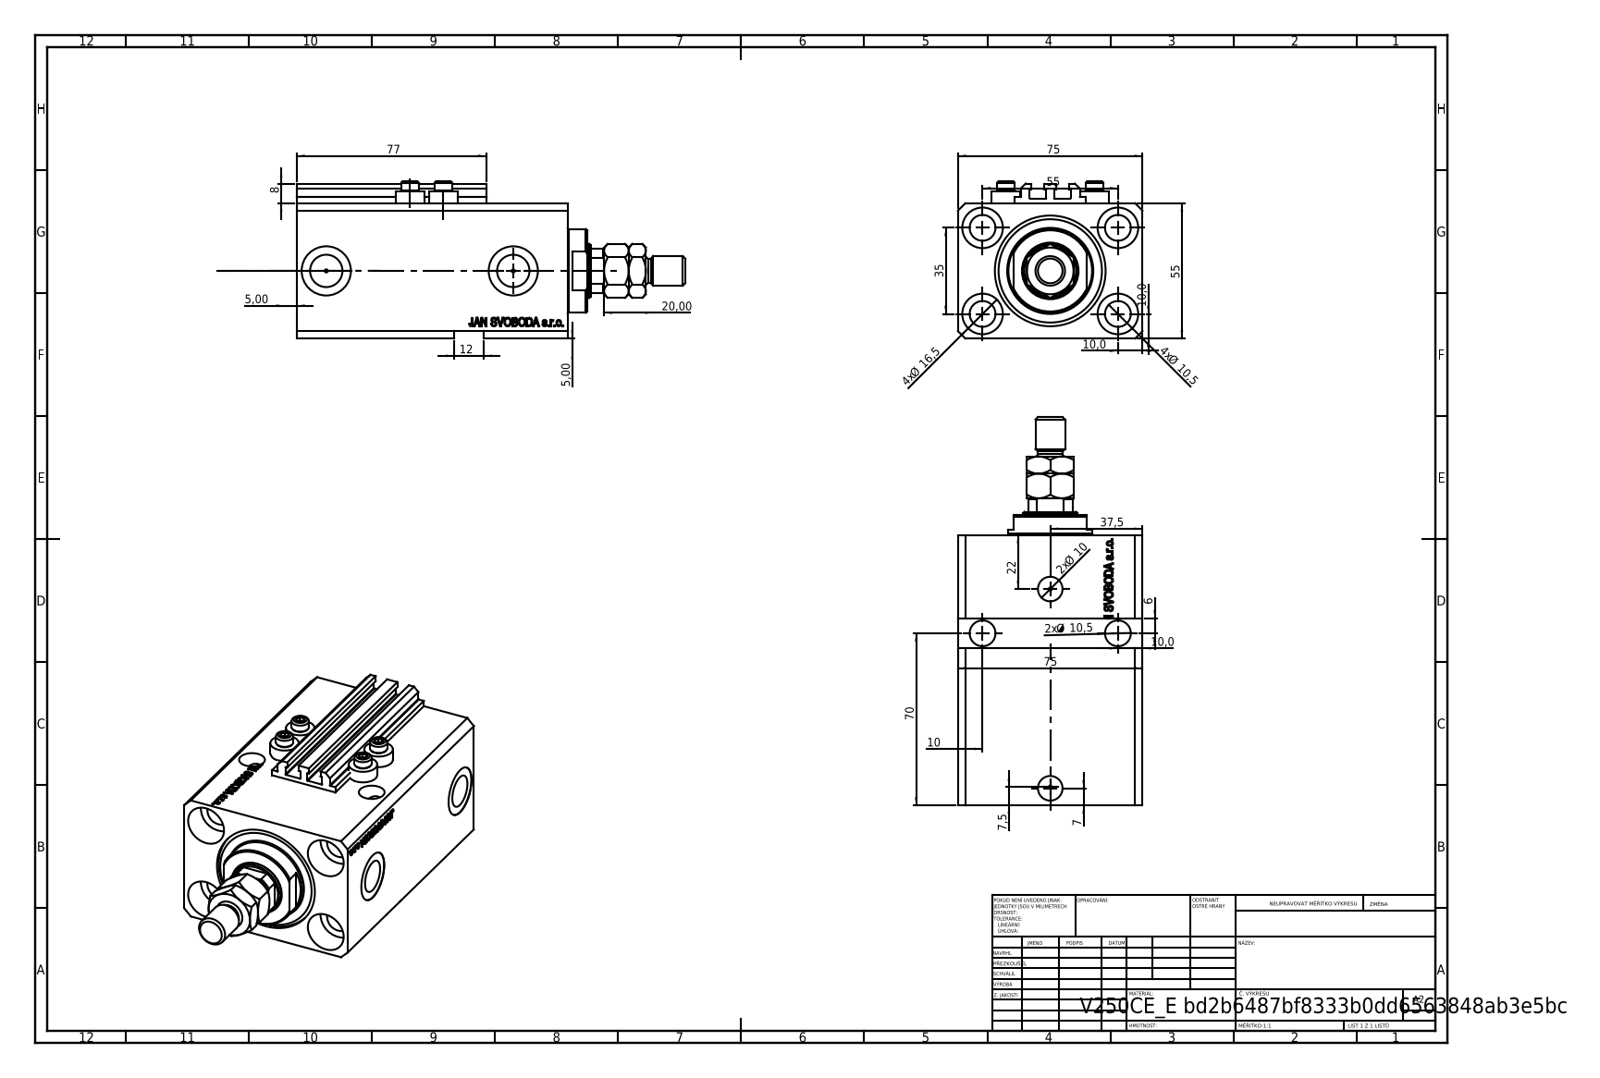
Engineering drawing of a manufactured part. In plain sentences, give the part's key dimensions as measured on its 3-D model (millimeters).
The part is named "V250CE_VC_E; V250CE_E_Body; MTA; V250CE_C_VCP (+1 more)". Its 3-D file was written by "SolidWorks 2019 (CONFIG_CONTROL_DESIGN)". It is 9 solids with 1129 faces: 533 planar, 142 cylindrical and 454 other. Overall it measures 157.9 by 75 by 64 millimeters. Its volume is 391 117 cubic millimeters and its surface area 100 168 square millimeters. Round holes: 7 of diameter 10.5, 4 of diameter 1.25, 4 of diameter 4, 4 of diameter 16.5, 2 of diameter 10, 2 of diameter 13.16, 2 of diameter 20, 1 of diameter 22, 1 of diameter 32, 1 of diameter 45. Round bosses or shafts: 4 of diameter 11.6, 4 of diameter 7, 1 of diameter 34, 1 of diameter 12, 1 of diameter 10. Partial cylindrical surfaces (rounded edges, fillets, slot ends): 10 of radius 0.2, 1 of radius 10.5. The main face-to-face distances are 55, 75, 110, 82.9, 27.1, 9.9, 3, 73, 100.1, 2.5. The hole center spacings are 32.6, 55, 13.6, 14.09, 25.81, 32.87, 33.62, 35.
